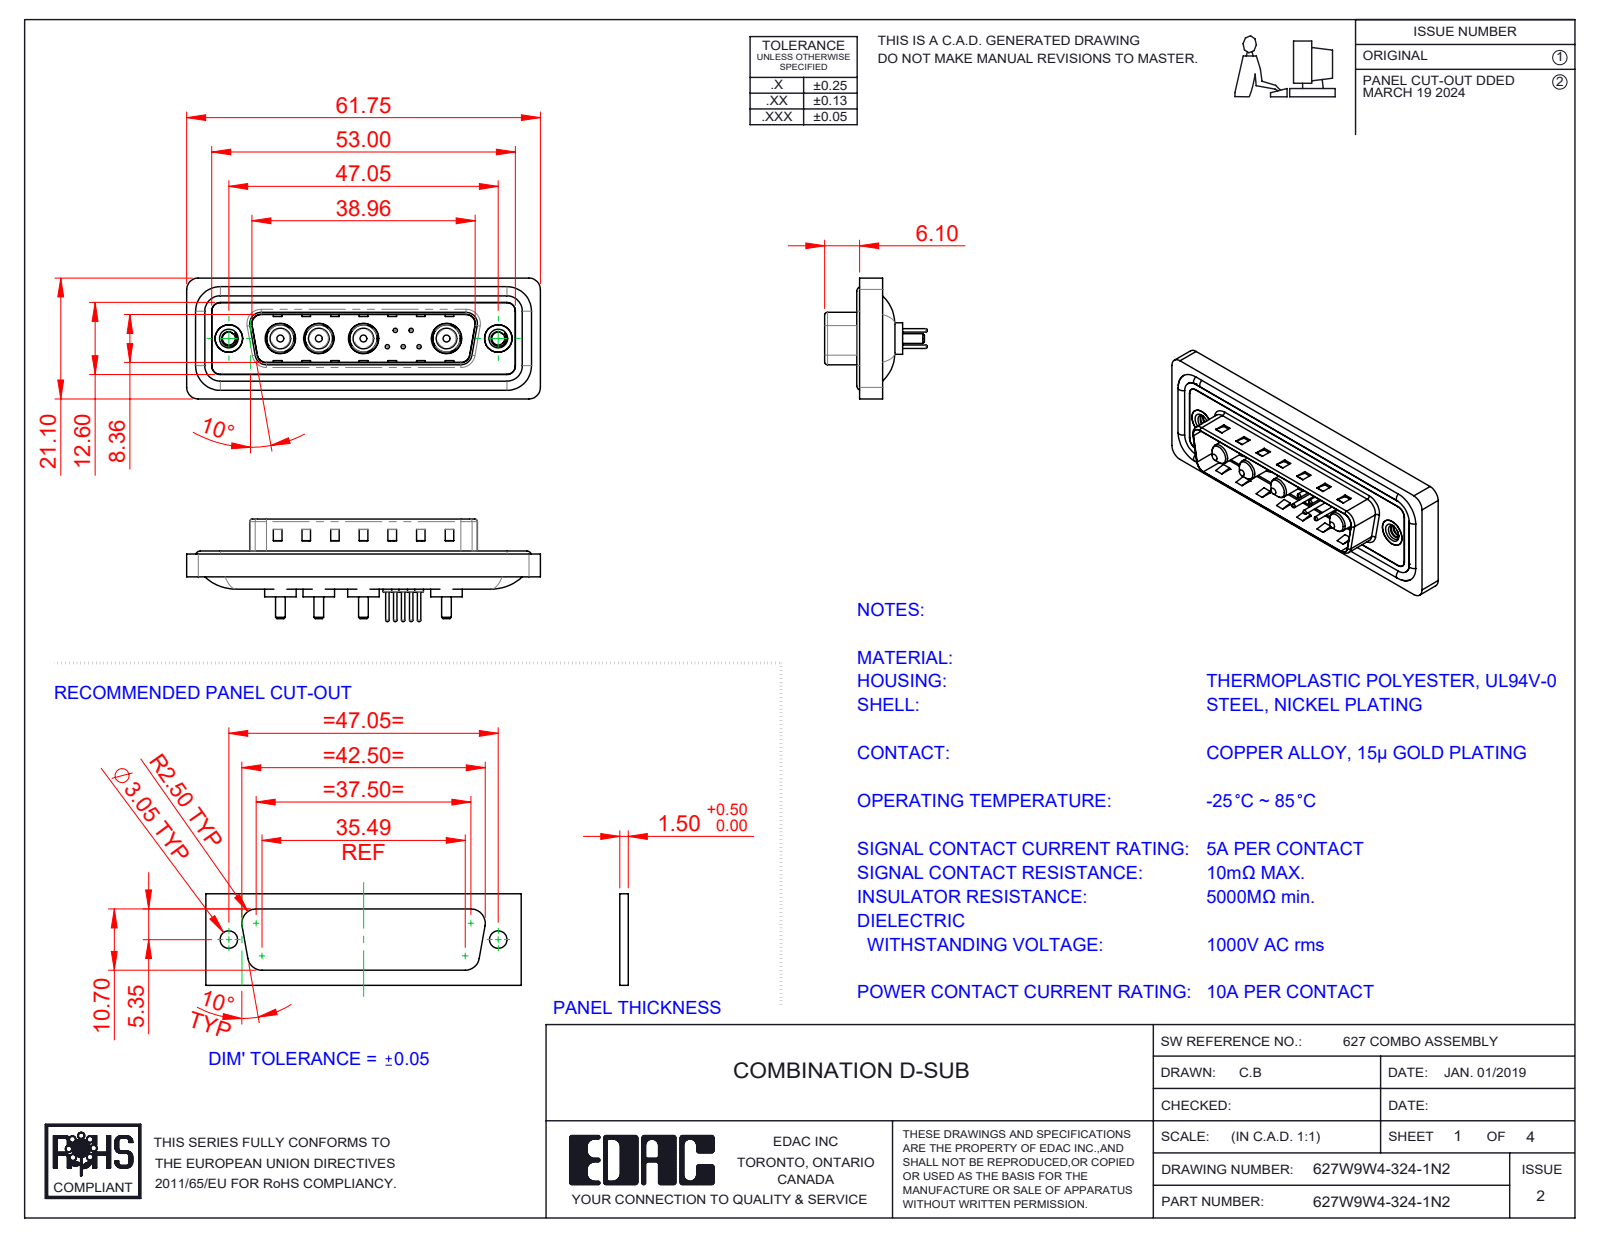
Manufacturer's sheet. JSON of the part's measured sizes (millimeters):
{"part_name": "627Combo Housing_9W4; Power Pin_10A S; 627Combo Shell Front_25 Contacts; 627W9W4-324-1N2 (+5 more)", "step_written_by": "SolidWorks 2023 (CONFIG_CONTROL_DESIGN)", "units": "millimeters", "bodies": {"solids": 20, "faces": 824, "planar": 284, "cylindrical": 334, "other": 206}, "overall_size": [61.75, 21.1, 17.9], "volume_mm3": 7345, "surface_area_mm2": 11785, "round_holes": [[0.75, 5], [1.6, 5], [2, 5], [4.85, 4], [5.3, 4], [2.26, 2], [4, 2], [4.8, 2], [5, 2]], "round_bosses_or_shafts": [[1.5, 5], [0.6, 5], [5.5, 4], [5.2, 4], [4.75, 4], [3.75, 4], [3.6, 4], [1.7, 4]], "partial_cylinders_radius": [[1.5, 22], [2, 18], [0.5, 8], [1.6, 8], [0.25, 4], [0.6, 4], [0.65, 4], [0.9, 4]], "face_to_face_distances": [0.4, 1.5, 1.1, 0.5, 3.1, 1.6, 2.9, 0.82, 9.58, 5.65], "hole_center_spacings": [3.16, 2.77, 5.04, 14.51, 2.78, 4.4, 4.41, 5]}
